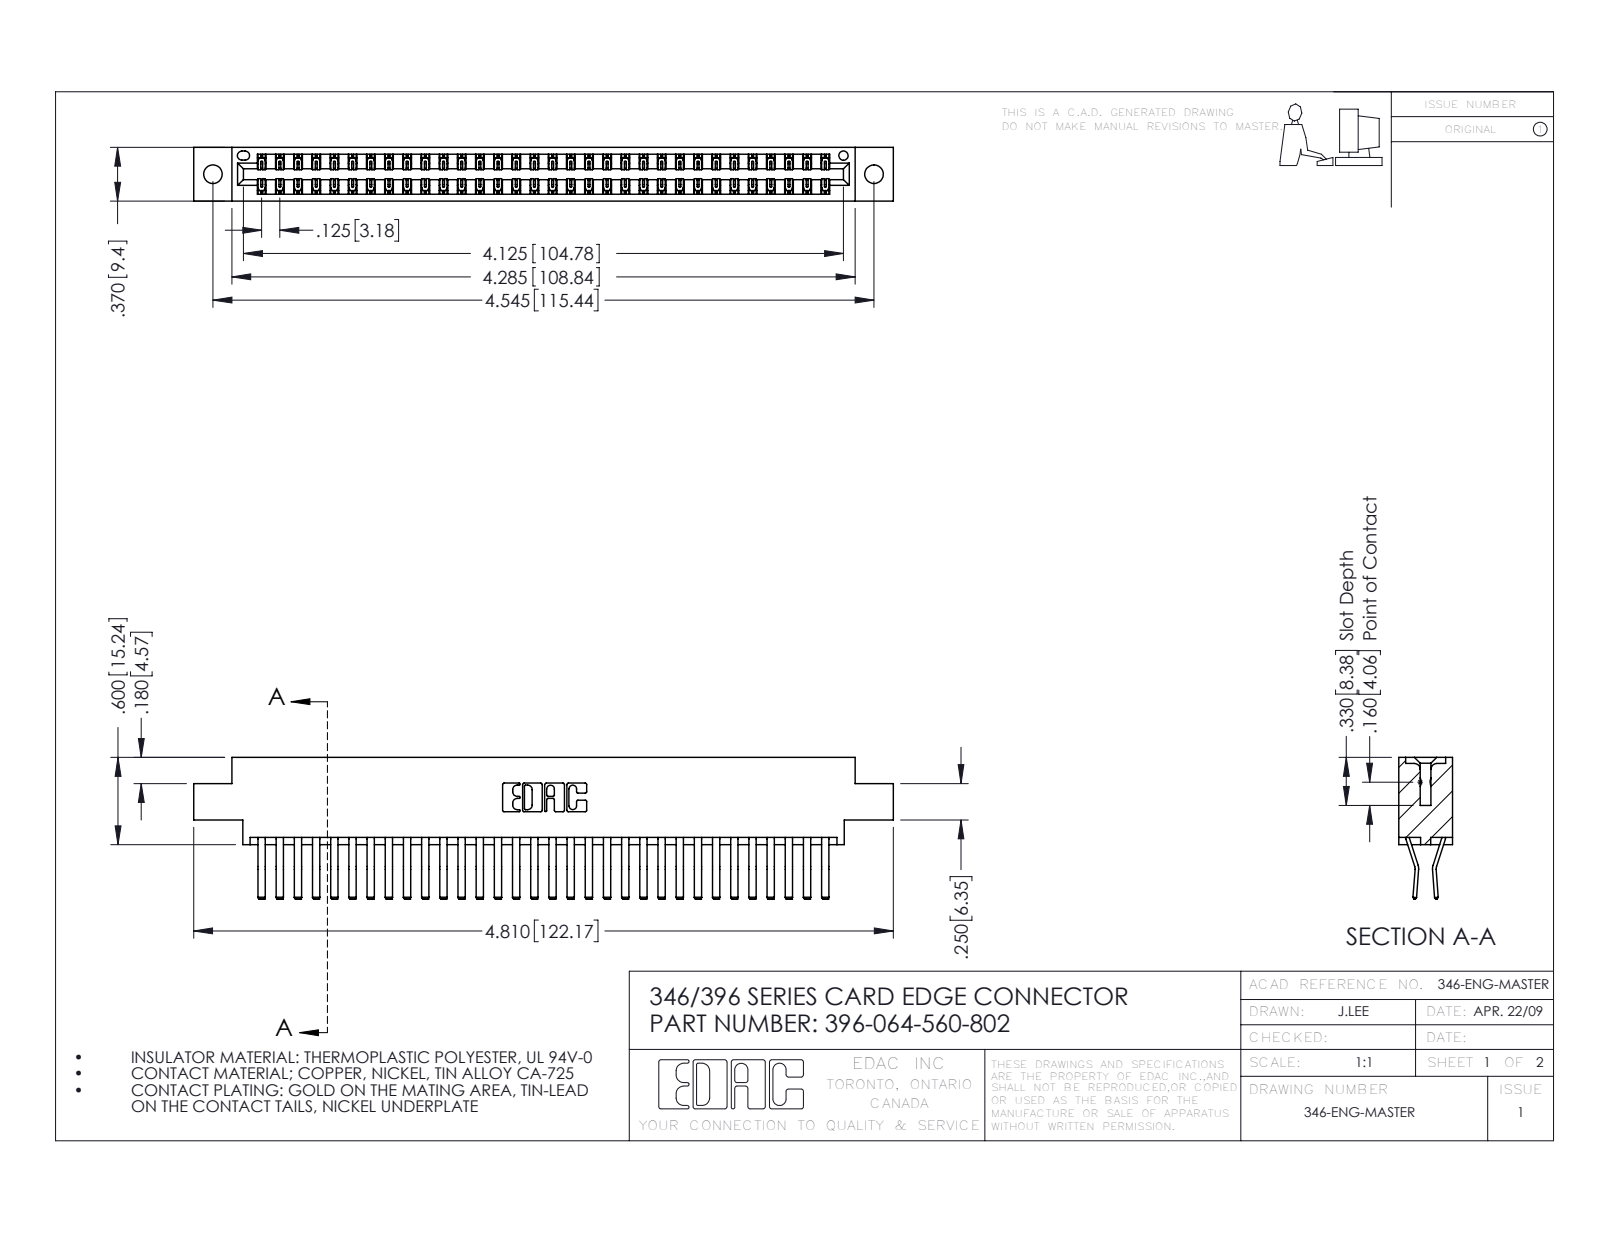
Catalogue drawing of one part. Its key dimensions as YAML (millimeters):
part_name: "346 Part_0.170 Offset - 0.128 Dia; 396-064-560-802; 345-292-001_560 Tail"
step_written_by: "SolidWorks 2016 (CONFIG_CONTROL_DESIGN)"
units: millimeters
bodies: {solids: 65, faces: 3582, planar: 2320, cylindrical: 1262, other: 0}
overall_size: [122.2, 24.8, 9.4]
volume: 12100
surface_area: 17460
round_holes:
  - {diameter: 3.3, count: 2}
  - {diameter: 1.6, count: 1}
partial_cylinders:
  - {radius: 0.2, count: 96}
  - {radius: 0.3, count: 22}
  - {radius: 0.2, count: 6}
  - {radius: 0.8, count: 6}
  - {radius: 0.7, count: 3}
  - {radius: 0.3, count: 2}
  - {radius: 0.4, count: 2}
  - {radius: 0.6, count: 2}
face_to_face_distances: [1.2, 8.2, 9.4, 0.6, 6.4, 1.8, 7.6, 7, 3.8, 5.6]
hole_center_spacings: [6.2, 110.2, 115.4]
